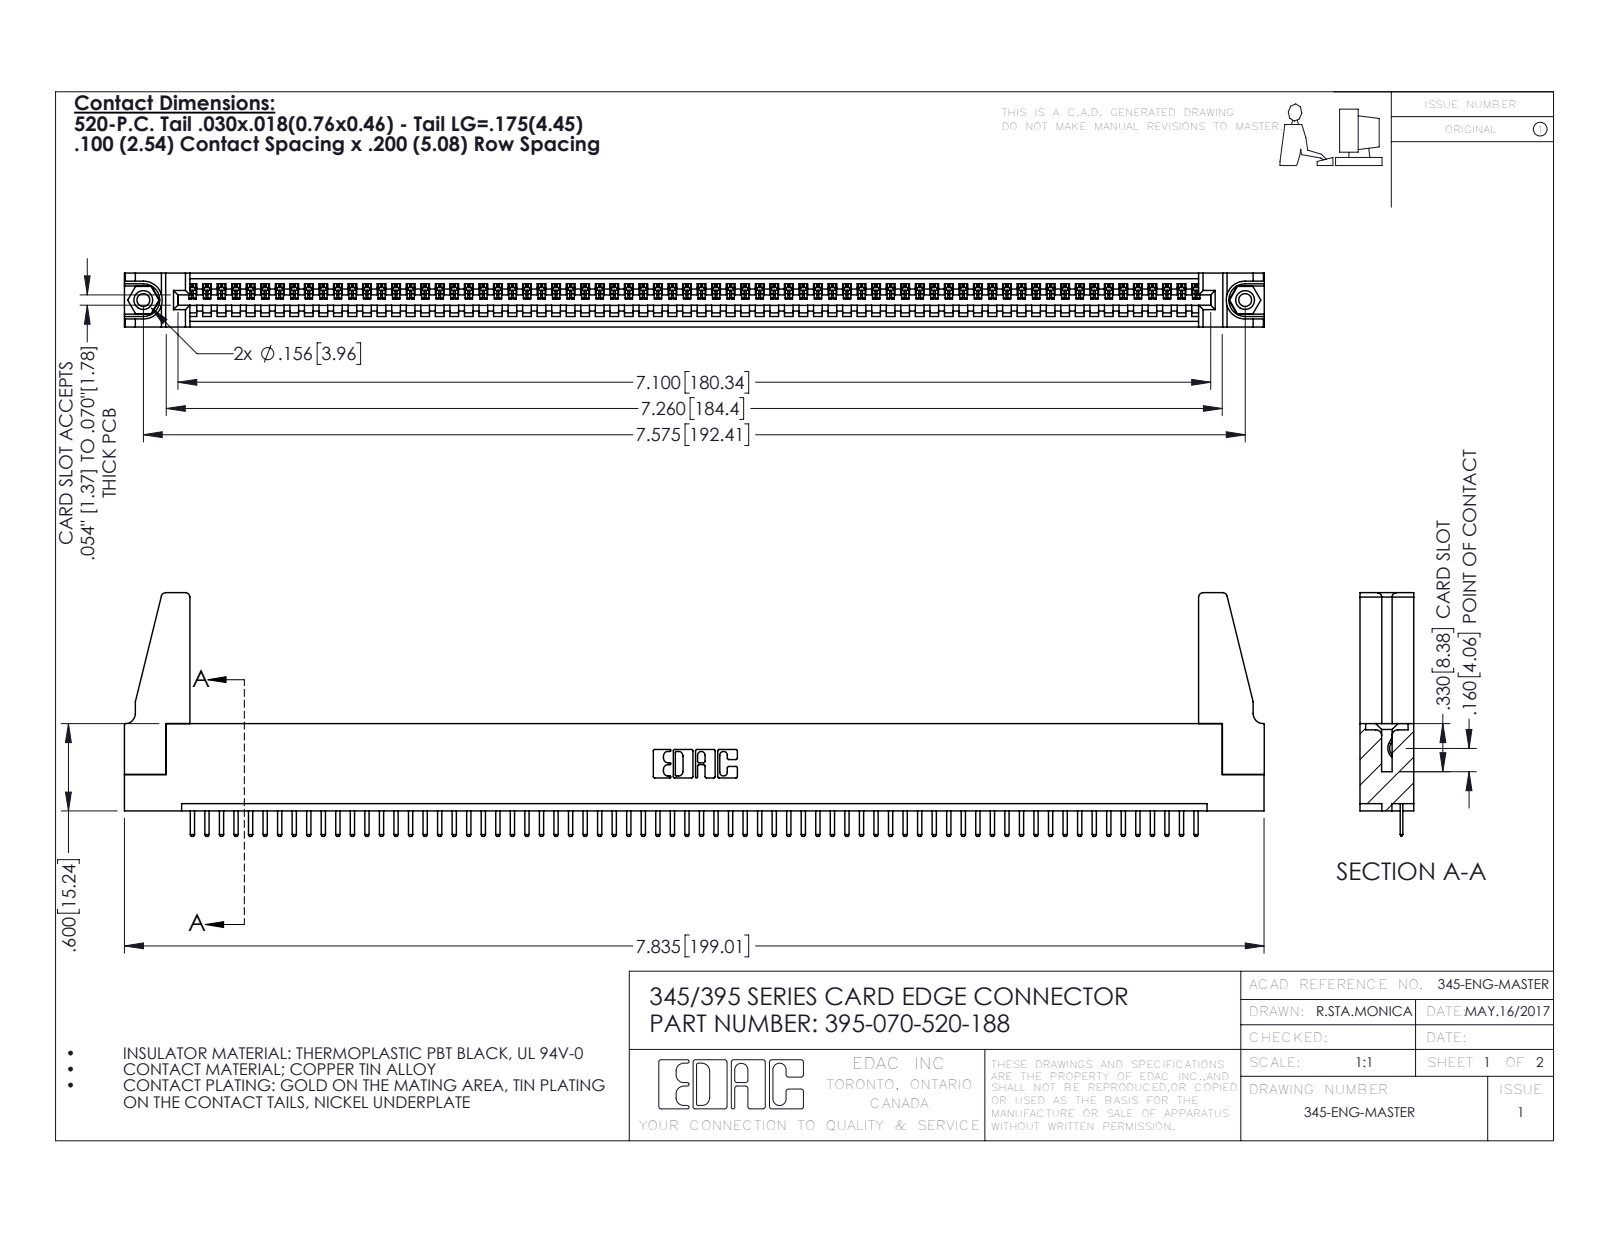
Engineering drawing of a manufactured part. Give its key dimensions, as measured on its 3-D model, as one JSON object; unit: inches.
{"part_name": "345-292-001_345-293-120; 395-070-520-188; 345-220-078_345-220-088; 345-250-001_345-250-001-102 (+1 more)", "step_written_by": "SolidWorks 2016 (CONFIG_CONTROL_DESIGN)", "units": "inches", "bodies": {"solids": 75, "faces": 4590, "planar": 3092, "cylindrical": 1482, "other": 16}, "overall_size": [7.836, 1.675, 0.37], "volume_in3": 1.354, "surface_area_in2": 43.42, "round_holes": [[0.089, 2], [0.125, 2], [0.156, 2], [0.064, 1]], "round_bosses_or_shafts": [[0.155, 2]], "partial_cylinders_radius": [[0.01, 142], [0.006, 140], [0.01, 22], [0.03, 8], [0.007, 6], [0.031, 6], [0.026, 3], [0.031, 2]], "face_to_face_distances": [0.072, 0.298, 0.37, 0.2, 0.098, 0.272, 0.025, 0.225, 0.072, 0.149], "hole_center_spacings": [0.27, 7.339, 7.575]}
